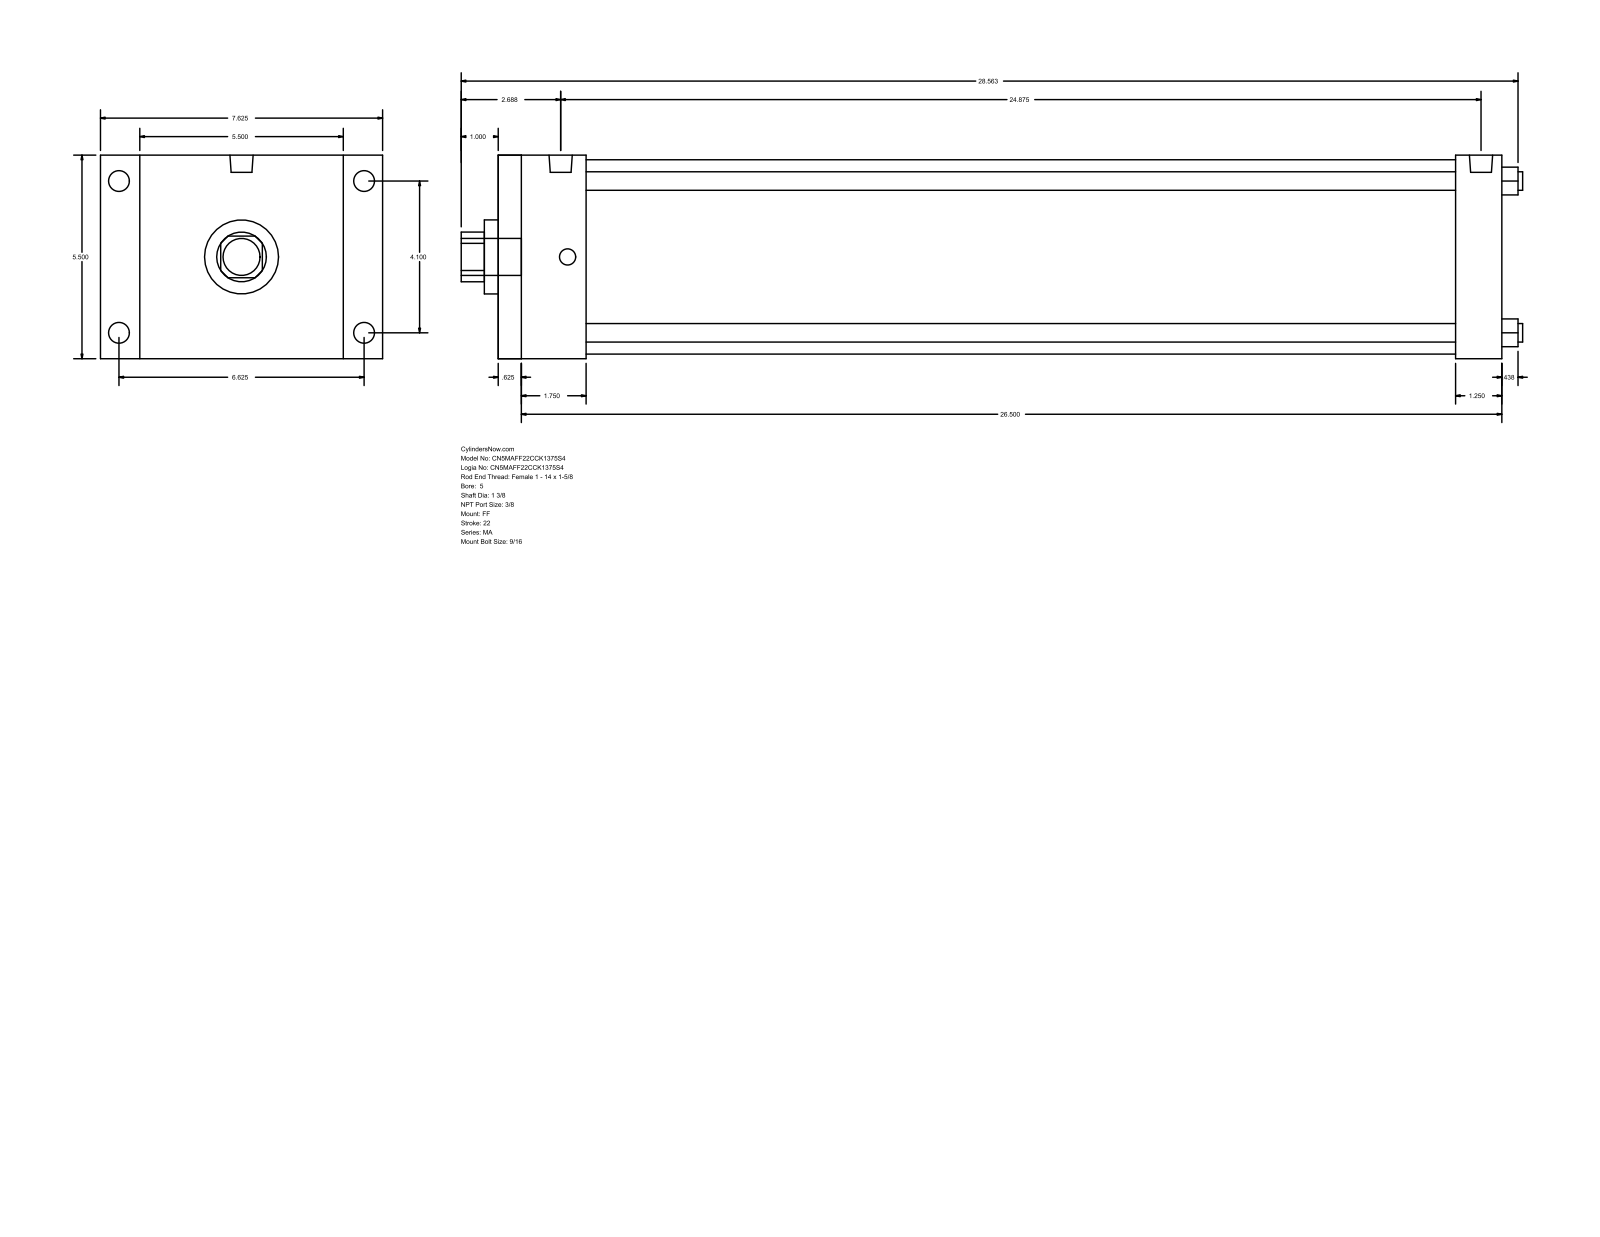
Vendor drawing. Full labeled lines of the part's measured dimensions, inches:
Part name (STEP PRODUCT): MA_FF__0500_1.375
STEP written by: GSSL Pune (CONFIG_CONTROL_DESIGN)
Units: inches
Bodies: 0 solids, 92 faces (64 planar, 28 cylindrical, 0 other)
Overall size (bounding box): 28.687 × 7.625 × 5.5
Round holes (diameter × count): ⌀0.5 ×4, ⌀1.375 ×1, ⌀2 ×1, ⌀5.25 ×1
Round bosses / shafts (diameter × count): ⌀0.563 ×4, ⌀0.437 ×4, ⌀0.627 ×2, ⌀1 ×1
Partial cylindrical surfaces — rounded edges, fillets, slot ends (radius × count): R0.672 ×1
Main face-to-face distances: 5.5, 27.125, 0.625, 26.5, 25.875, 25.25, 1.25, 2.375, 1.75, 23.5
Hole centre spacings: 2.899, 4.1, 5.798
